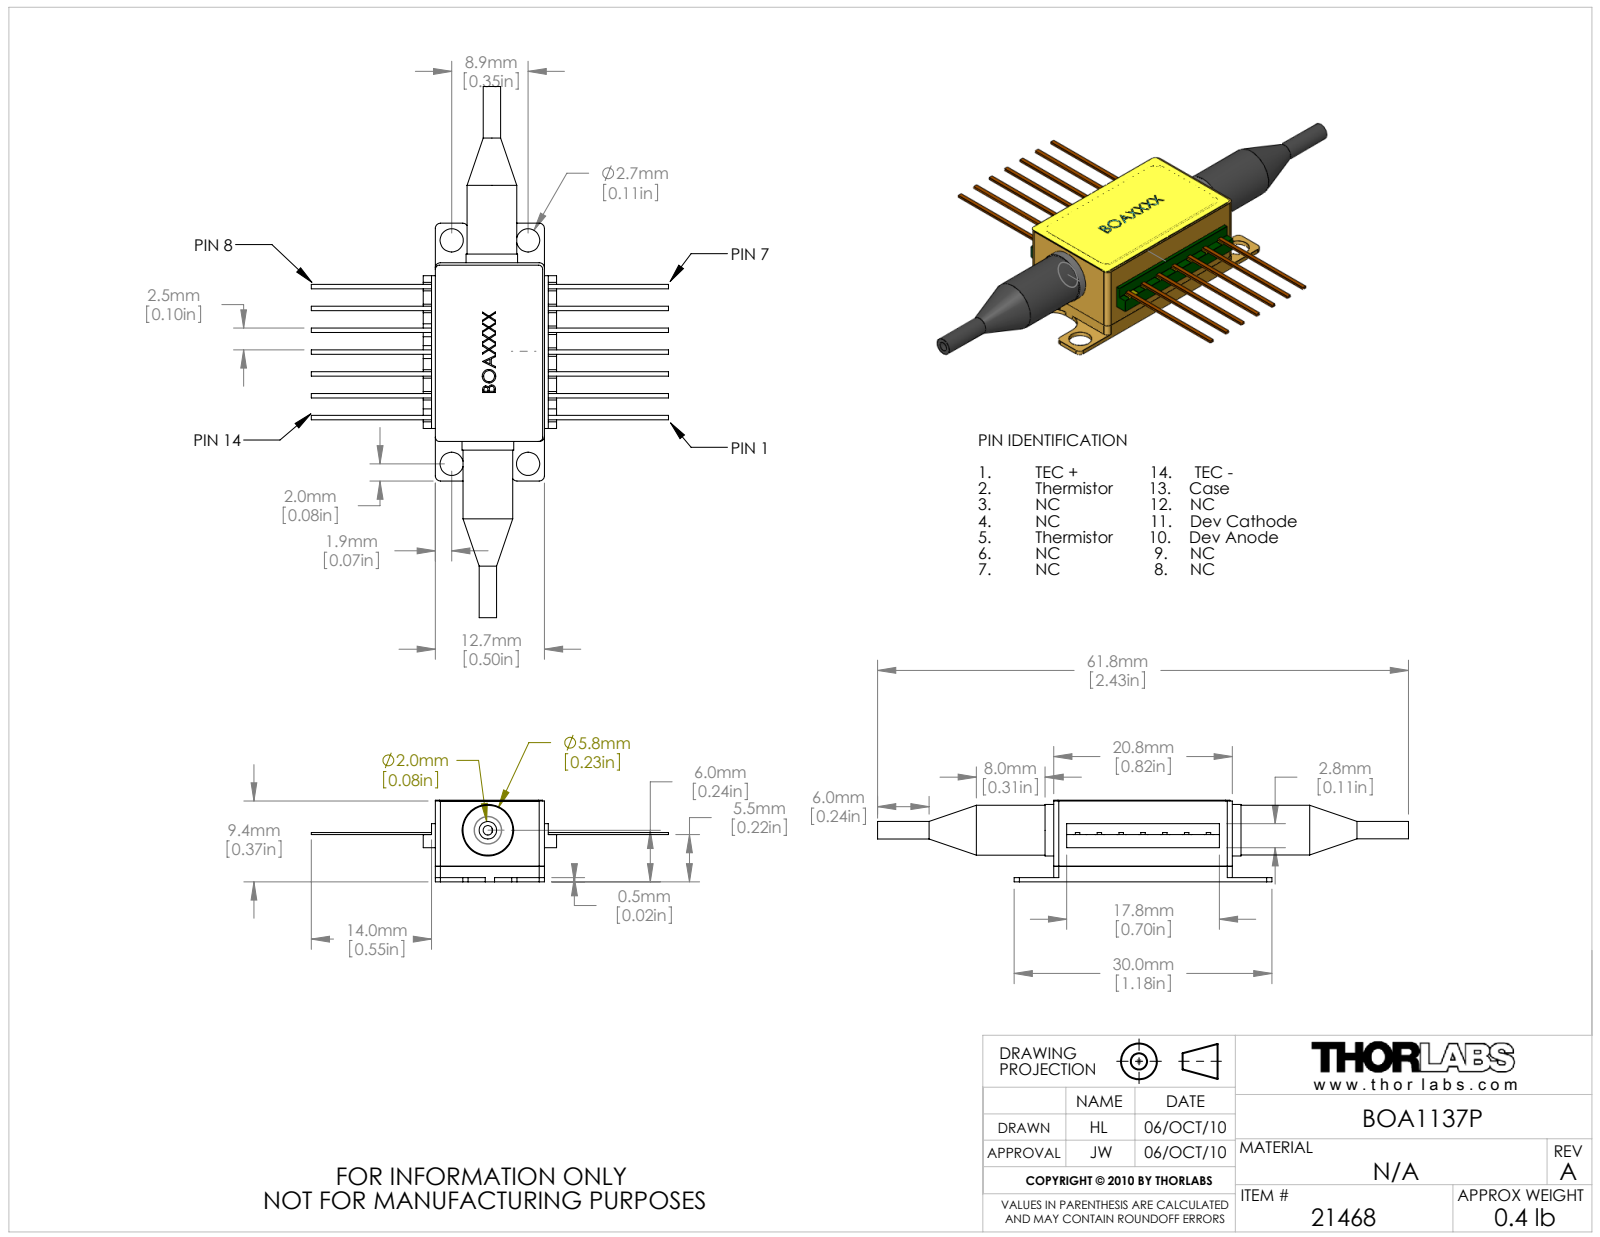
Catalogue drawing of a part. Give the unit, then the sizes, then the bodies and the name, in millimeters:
Units: millimetres
Overall size (bounding box): 61.8 × 41.6 × 9.5
Round holes (diameter × count): ⌀2.7 ×4, ⌀1.1 ×2, ⌀2.08 ×2, ⌀3.17 ×2, ⌀3.5 ×2, ⌀4.1 ×2
Round bosses / shafts (diameter × count): ⌀6 ×2, ⌀5.8 ×2, ⌀3.45 ×2, ⌀3.18 ×2, ⌀2.04 ×2, ⌀2 ×2
Partial cylindrical surfaces — rounded edges, fillets, slot ends (radius × count): R0.6 ×12, R1 ×12, R0.2 ×4, R0.5 ×4, R2 ×4
Main face-to-face distances: 1, 9.51, 3.7, 7.6, 3.9, 1.8, 7.71, 9.2, 7.4, 0.31
Hole centre spacings: 8.9, 26, 27.48, 0.47
Volume: 1 674 mm³ · Surface area: 4 547 mm²
Bodies: 27 solids, 484 faces (347 planar, 96 cylindrical, 41 other)
Part name (STEP PRODUCT): RevAGRIN Lens1_SLW2.0 0.25P 8D 1560nm; RevAsnout; 32110-000_20130-000 25mm; Spout tube (+8 more)
STEP written by: SolidWorks 2009 (AUTOMOTIVE_DESIGN)
